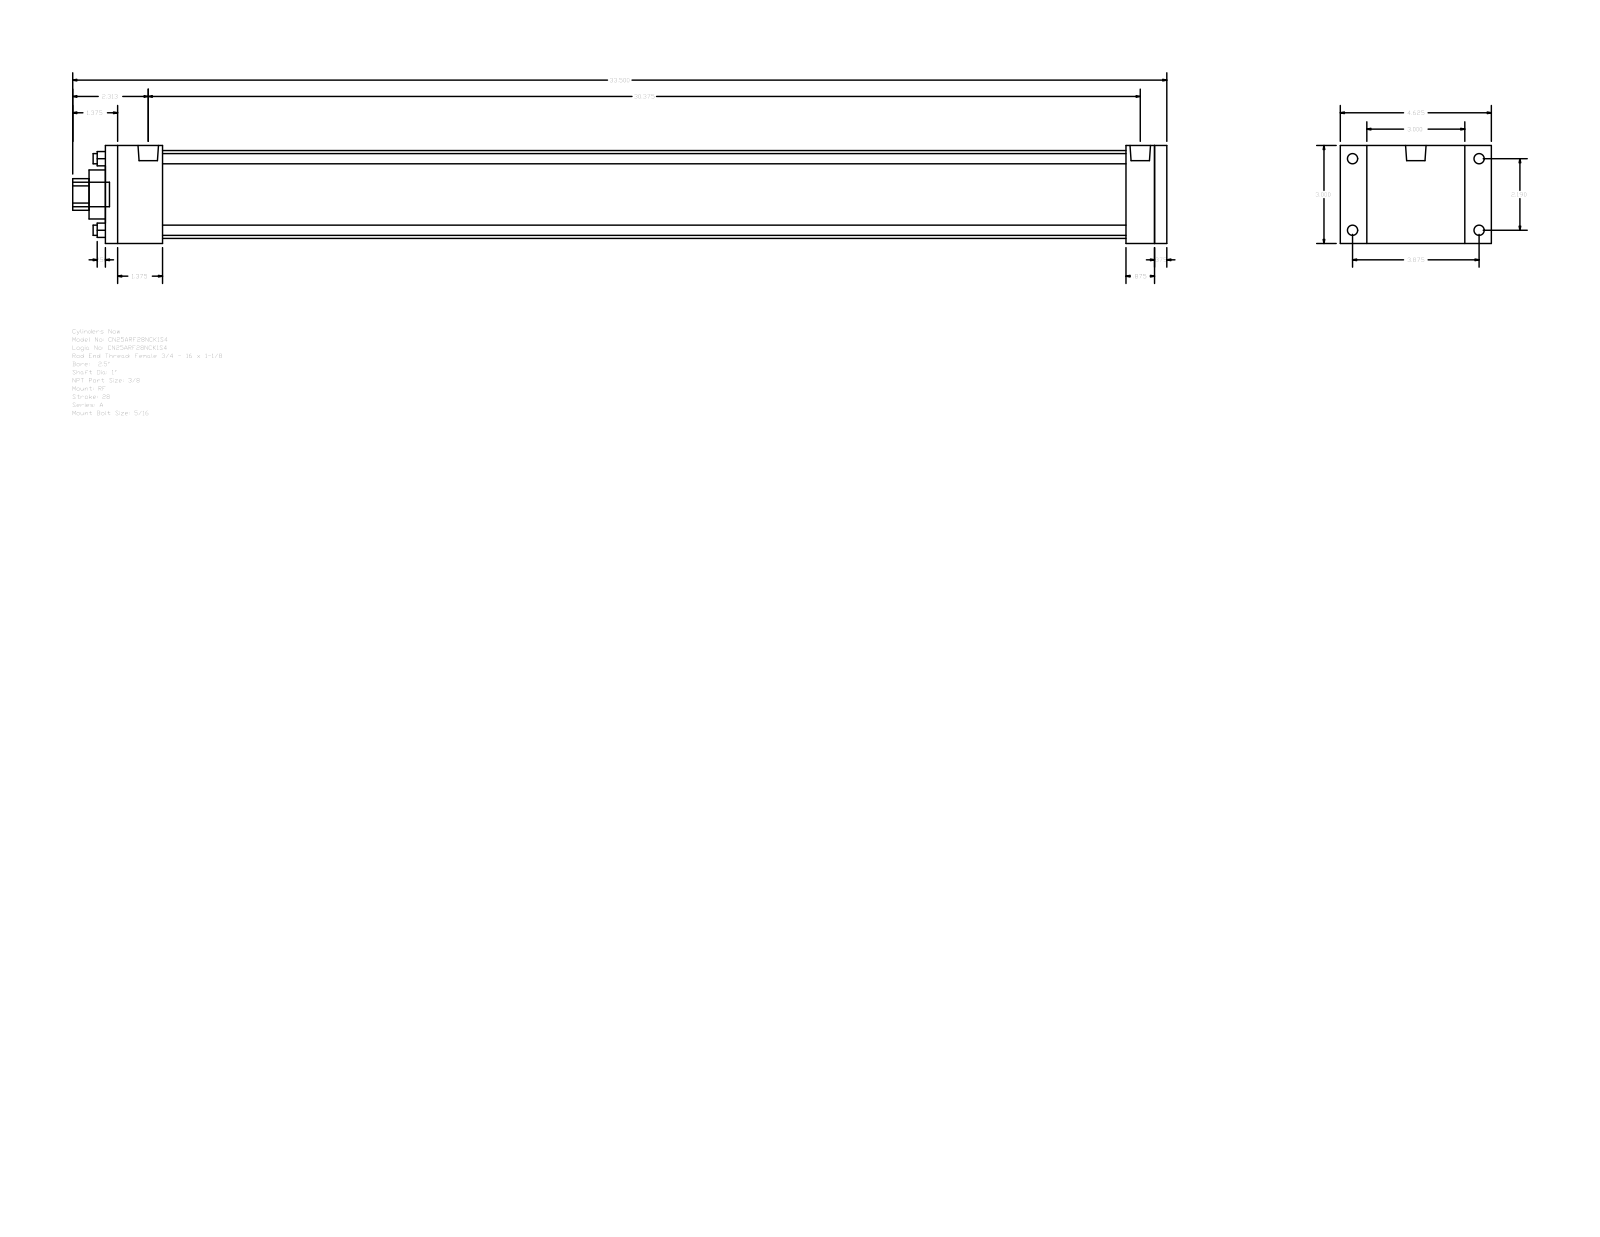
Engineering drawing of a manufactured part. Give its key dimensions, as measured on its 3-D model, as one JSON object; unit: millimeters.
{"part_name": "A_RF__0250_1", "step_written_by": "GSSL Pune (CONFIG_CONTROL_DESIGN)", "units": "millimeters", "bodies": {"solids": 0, "faces": 92, "planar": 64, "cylindrical": 28, "other": 0}, "overall_size": [850.9, 117.47, 76.2], "round_holes": [[7.94, 4], [25.4, 1], [38.1, 1], [68.33, 1]], "round_bosses_or_shafts": [[7.94, 4], [5.56, 4], [15.93, 2], [19.05, 1]], "partial_cylinders_radius": [[12.29, 1]], "face_to_face_distances": [76.2, 825.5, 9.52, 815.98, 44.45, 793.75, 749.3, 771.53, 781.05, 22.23], "hole_center_spacings": [39.33, 55.62, 78.66]}
